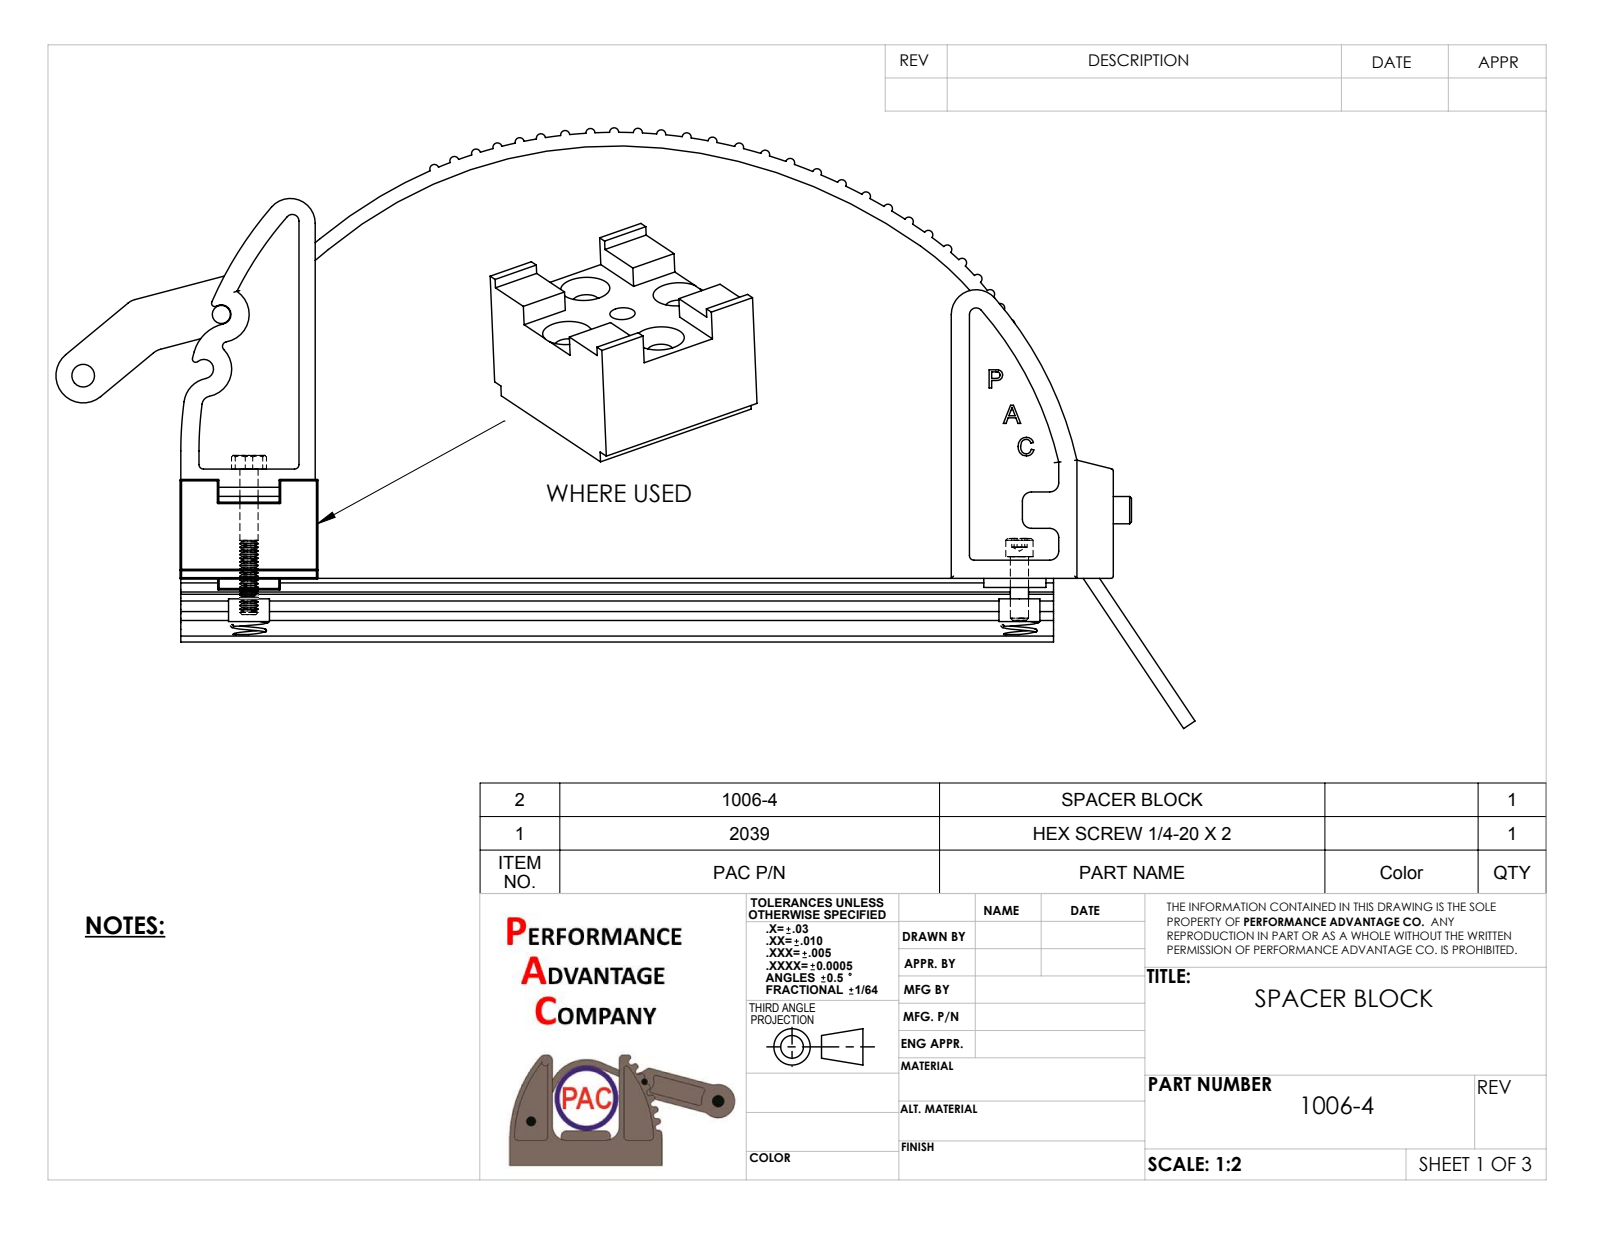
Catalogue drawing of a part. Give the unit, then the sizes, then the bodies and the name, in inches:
Units: inches
Overall size (bounding box): 2.063 × 1.875 × 1.499
Round holes (diameter × count): ⌀0.266 ×4, ⌀0.26 ×1
Main face-to-face distances: 1.875, 2.062, 1.037, 1.252, 0.215, 0.115, 0.149, 1.186, 1.401, 0.513
Hole centre spacings: 0.687, 0.972, 1.375
Volume: 4.023 in³ · Surface area: 22.48 in²
Bodies: 1 solid, 53 faces (35 planar, 10 cylindrical, 8 other)
Part name (STEP PRODUCT): 1006-4
STEP written by: SolidWorks 2010 (CONFIG_CONTROL_DESIGN)
